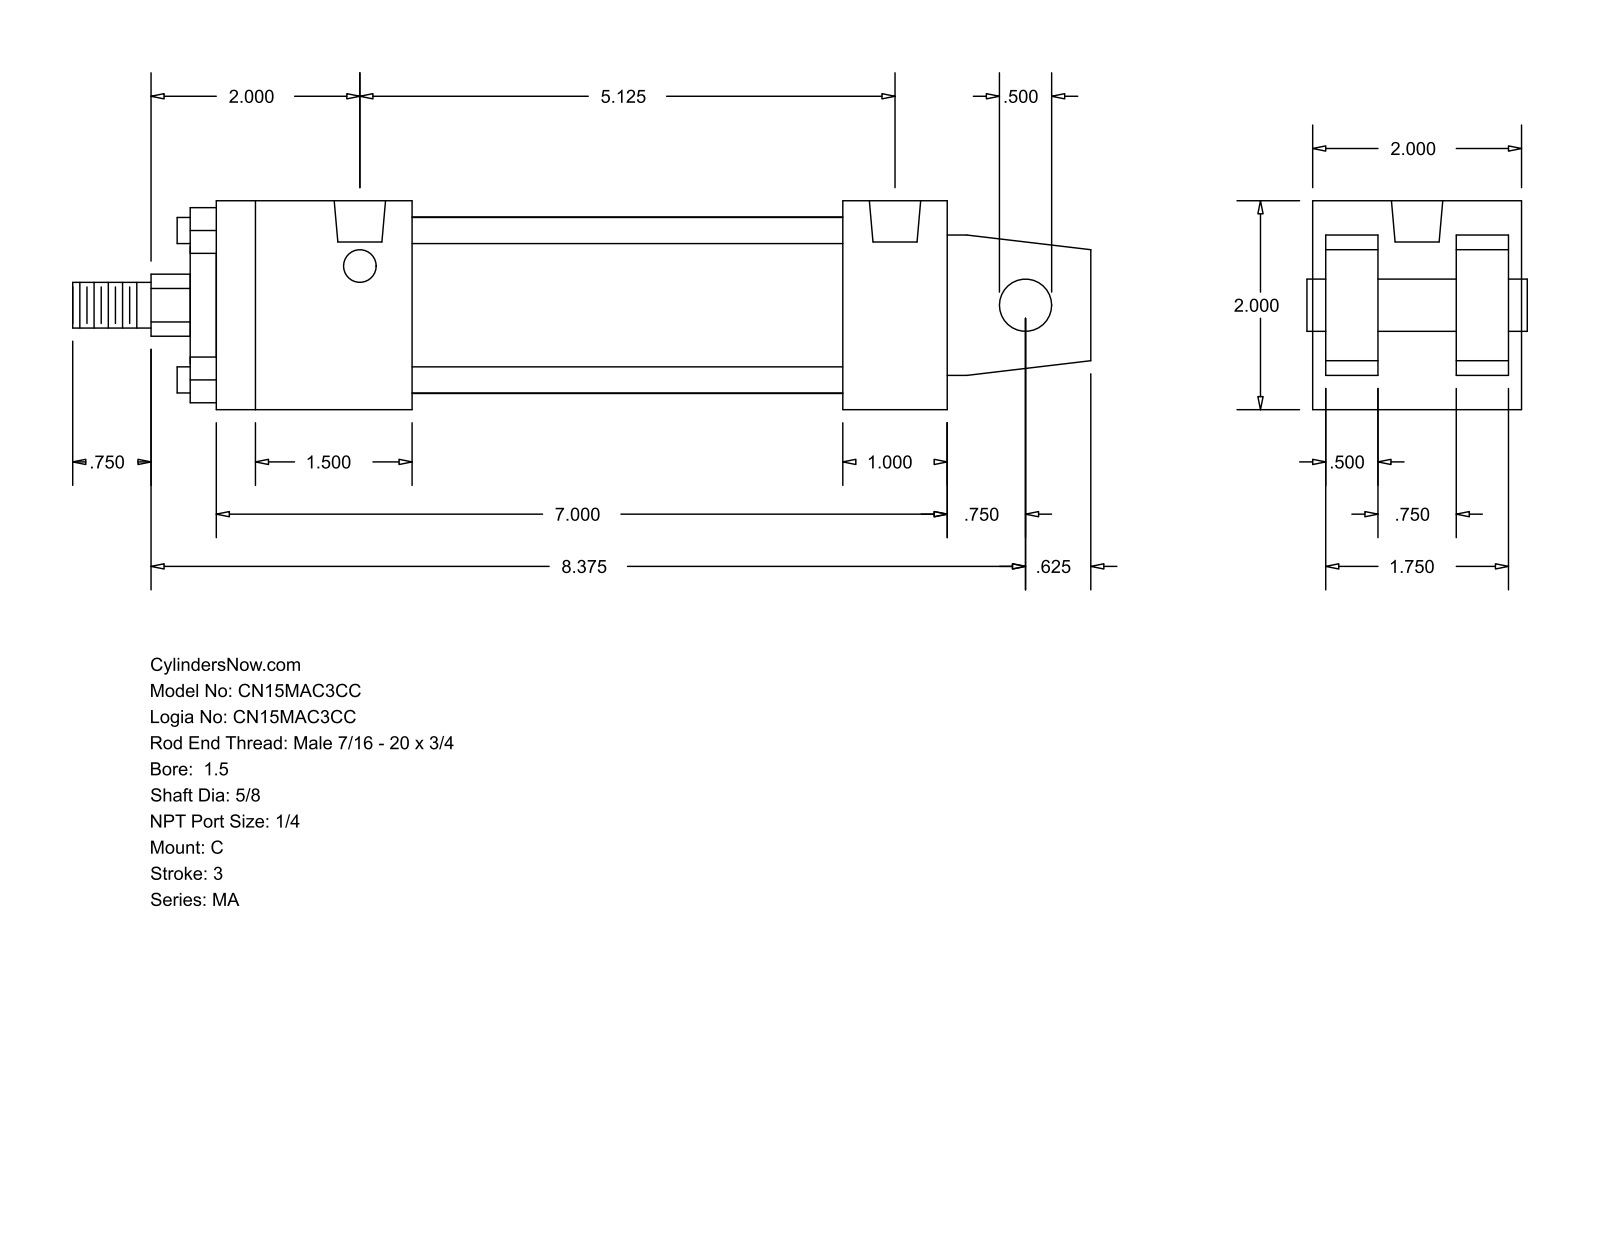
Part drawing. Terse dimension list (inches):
name: MA_C__0150_0.625
written by: GSSL Pune (CONFIG_CONTROL_DESIGN)
unit: in
bodies: 0 solids, 103 faces (76 planar, 27 cylindrical, 0 other)
size: 9.75 × 2 × 2
holes: 4× ⌀0.313, 2× ⌀0.492
bosses: 4× ⌀0.25, 1× ⌀1.69, 1× ⌀1.125, 1× ⌀0.625, 1× ⌀0.5, 1× ⌀0.437
rounds: 1× R0.297
face distances: 2, 0.5, 1.375, 0.625, 0.125, 1.875, 1.25, 7, 1, 6
hole spacings: 5.125
